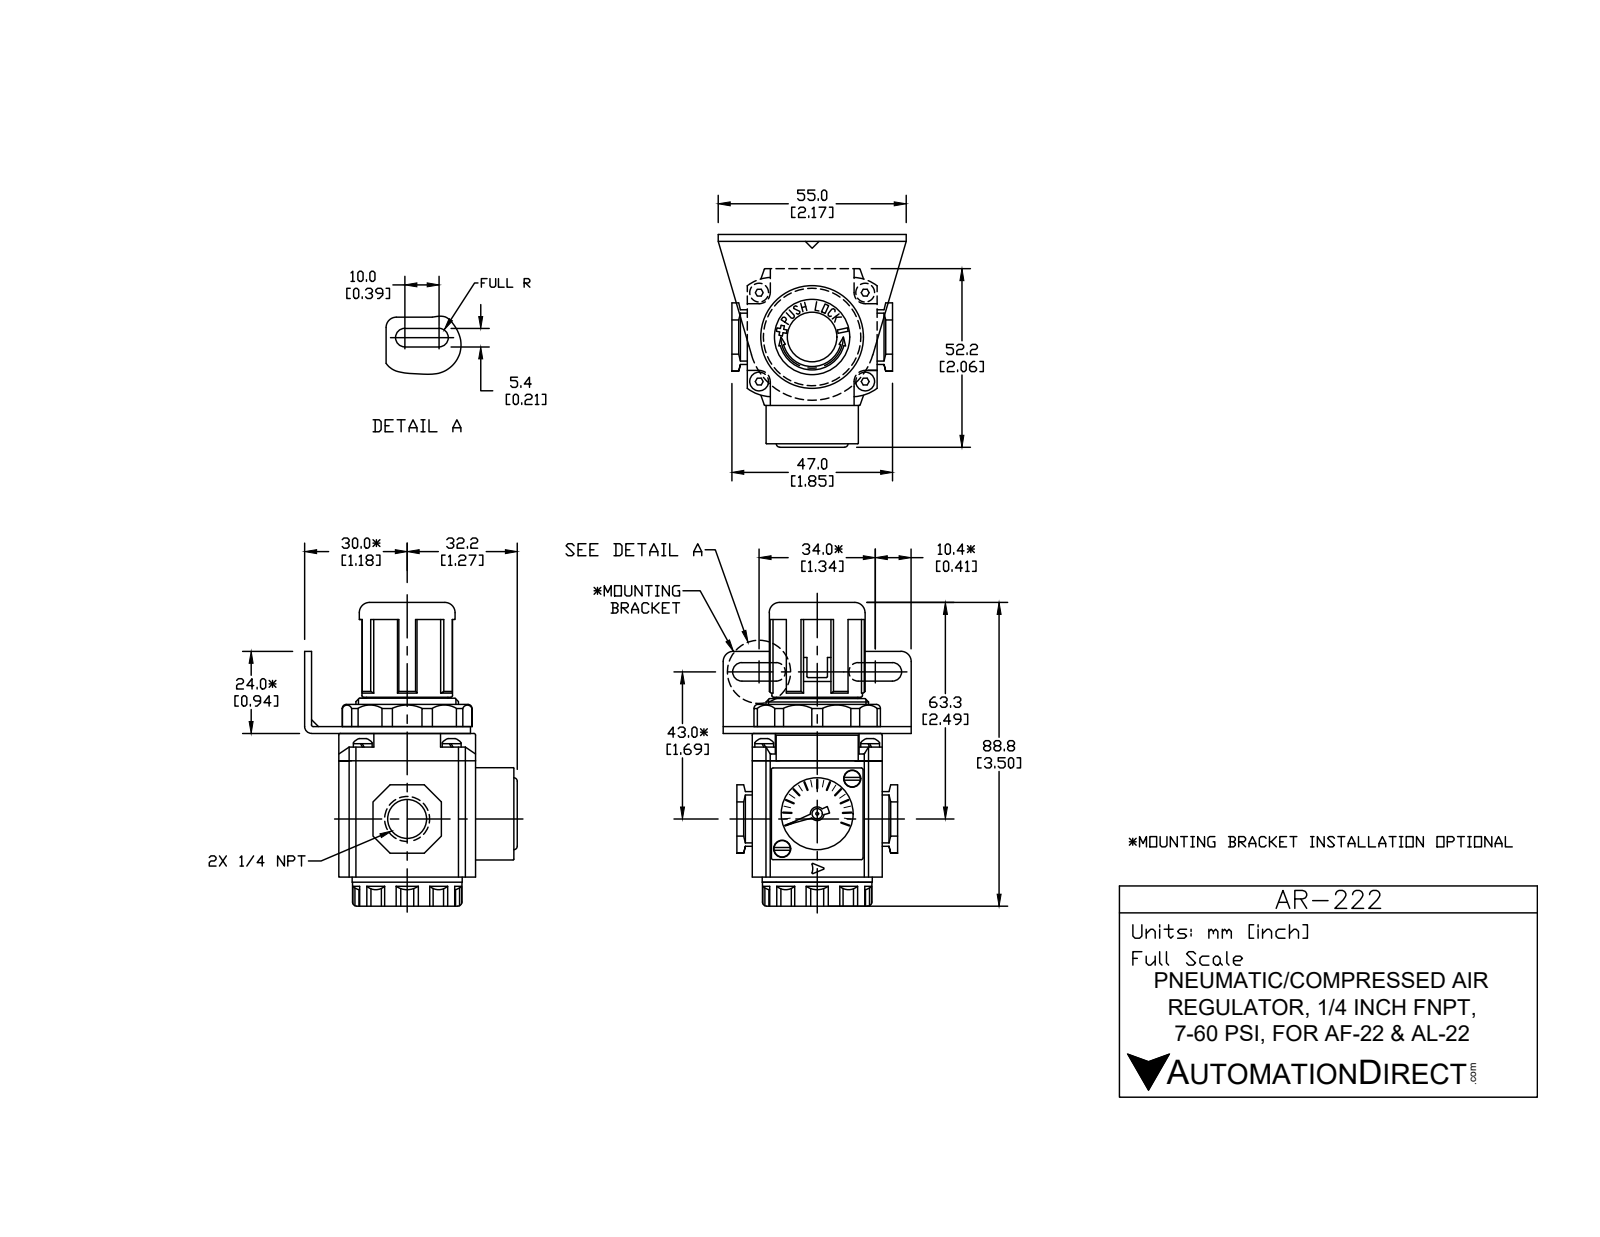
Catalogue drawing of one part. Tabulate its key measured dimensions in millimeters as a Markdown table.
| quantity | value |
| --- | --- |
| part name | AR-222 |
| STEP written by | SolidWorks 2015 (CONFIG_CONTROL_DESIGN) |
| units | millimeters |
| bodies | 14 solids, 491 faces (326 planar, 133 cylindrical, 32 other) |
| overall size | 88.8 × 62 × 55 |
| volume | 100 911 mm³ |
| surface area | 29 790 mm² |
| round holes (diameter × count) | 3 × 6, 2 × 1, 11.13 × 1, 21 × 1, 22 × 1, 30 × 1 |
| round bosses / shafts (diameter × count) | 5.5 × 4, 2.7 × 2, 32 × 1, 31.36 × 1, 28 × 1, 23.8 × 1, 14 × 1, 4 × 1 |
| partial cylindrical surfaces (radius × count) | 1.2 × 10, 1 × 8, 3.25 × 6, 0.3 × 4, 2.75 × 4, 12 × 4, 0.2 × 3, 2 × 1 |
| main face-to-face distances | 2, 42, 10, 44, 39, 40, 38, 50, 1, 11 |
| hole center spacings | 20.23, 14.5, 26, 31, 40.46, 28.99 |
